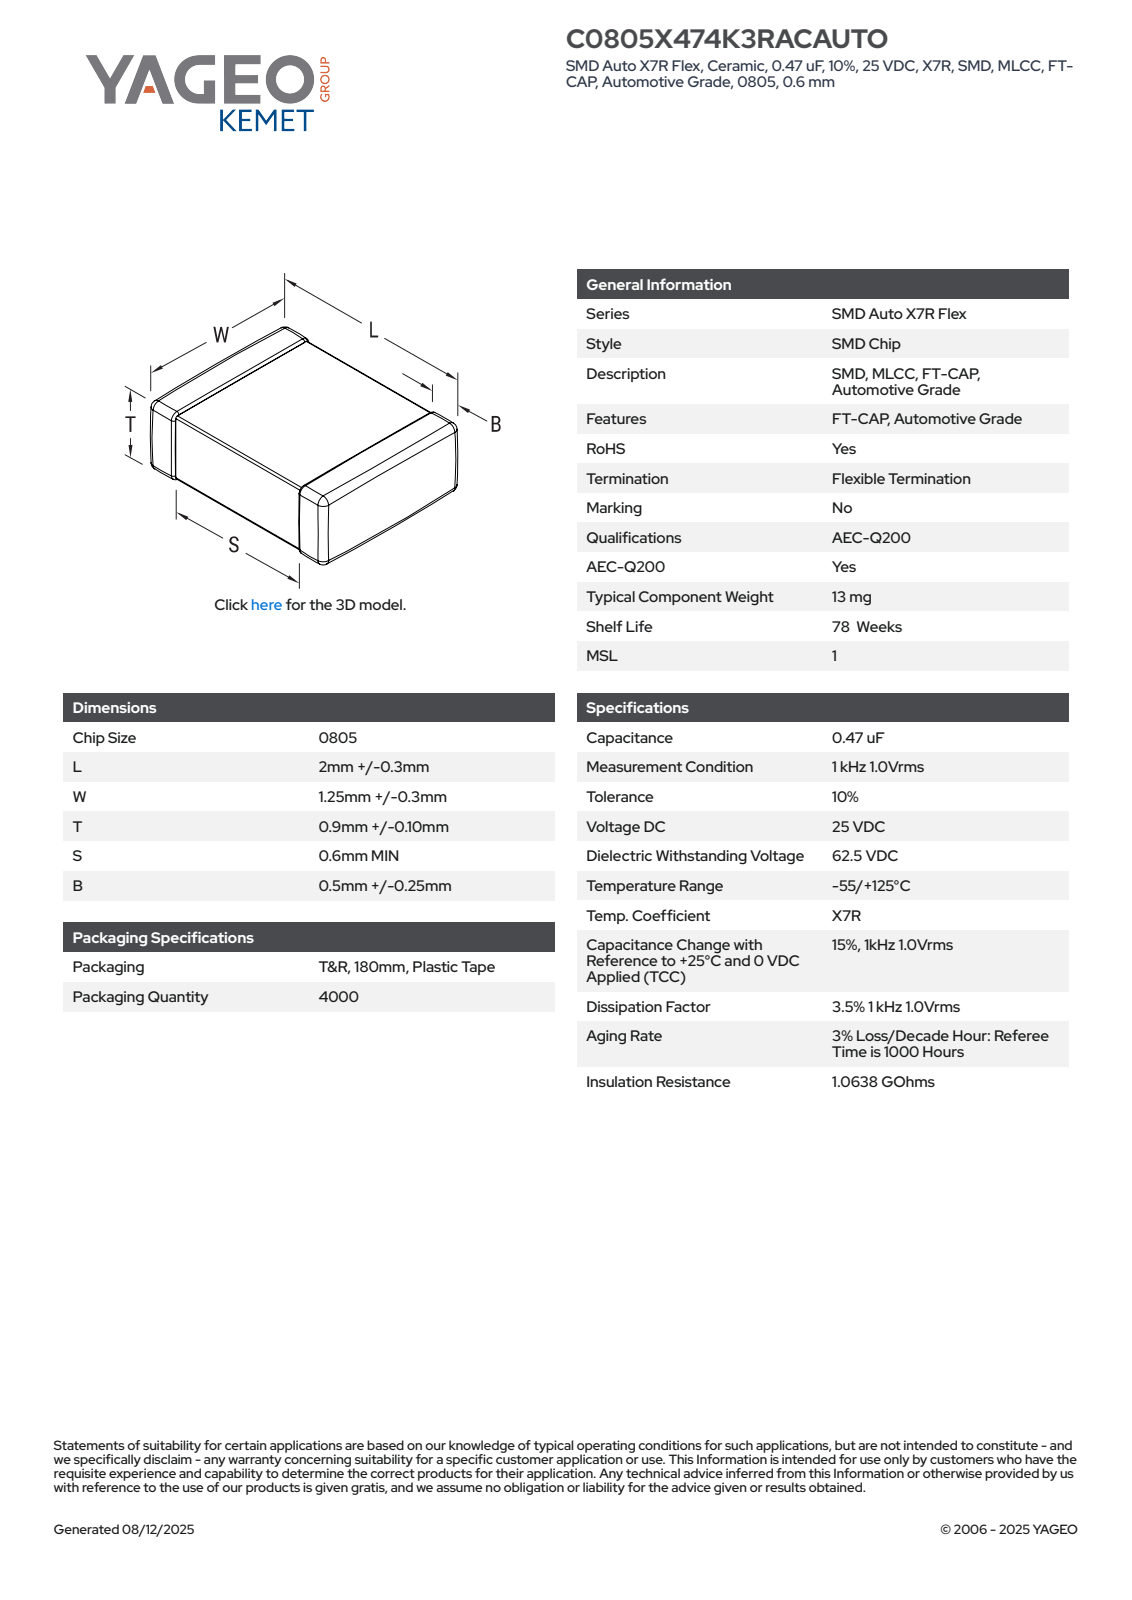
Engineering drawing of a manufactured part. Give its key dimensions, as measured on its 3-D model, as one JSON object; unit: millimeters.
{"part_name": "CCS_CCSTD_0805_L2.3W1.55T1B0.5", "step_written_by": "SolidWorks 2014 (AUTOMOTIVE_DESIGN)", "units": "millimeters", "bodies": {"solids": 4, "faces": 125, "planar": 71, "cylindrical": 38, "other": 16}, "overall_size": [2.3, 1.55, 1], "volume_mm3": 3, "surface_area_mm2": 15, "face_to_face_distances": [0.97, 0.94, 1.52, 2.3, 1, 1.49, 1.55, 1.06, 1.24, 1.01]}
